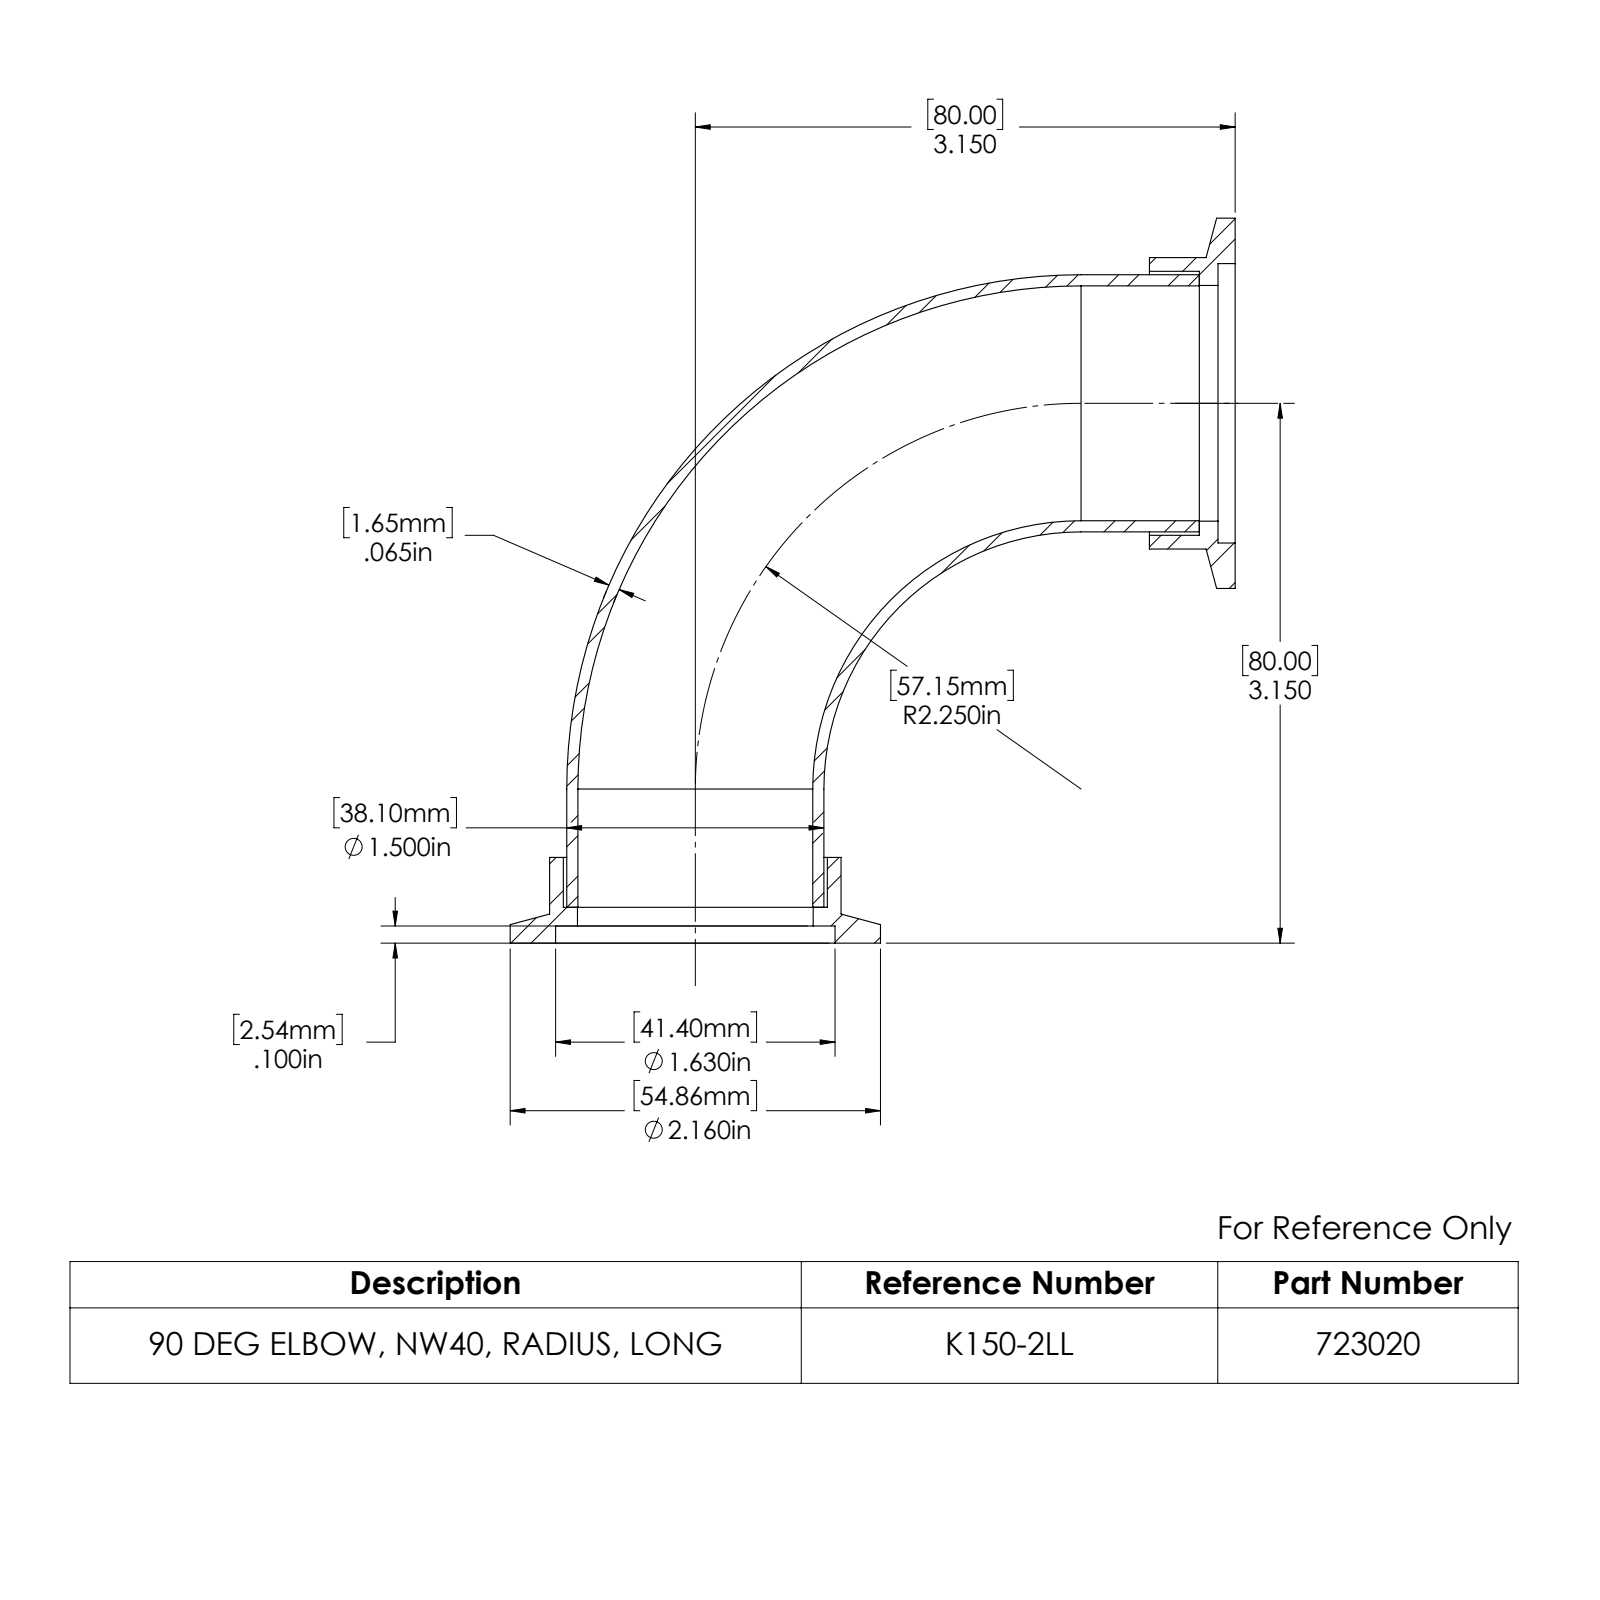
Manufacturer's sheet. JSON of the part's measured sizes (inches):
{"part_name": "723020; 403542; 972302", "step_written_by": "SolidWorks 2022 (AUTOMOTIVE_DESIGN)", "units": "inches", "bodies": {"solids": 3, "faces": 38, "planar": 10, "cylindrical": 20, "other": 8}, "overall_size": [3.539, 3.539, 2.16], "volume_in3": 1.864, "surface_area_in2": 51.04, "round_holes": [[1.375, 2], [1.54, 2], [1.63, 2]], "round_bosses_or_shafts": [[2.16, 2], [1.7, 2]], "face_to_face_distances": [0.1, 0.4, 0.5, 0.209, 0.209, 0.109, 0.109, 0.291, 0.291]}
